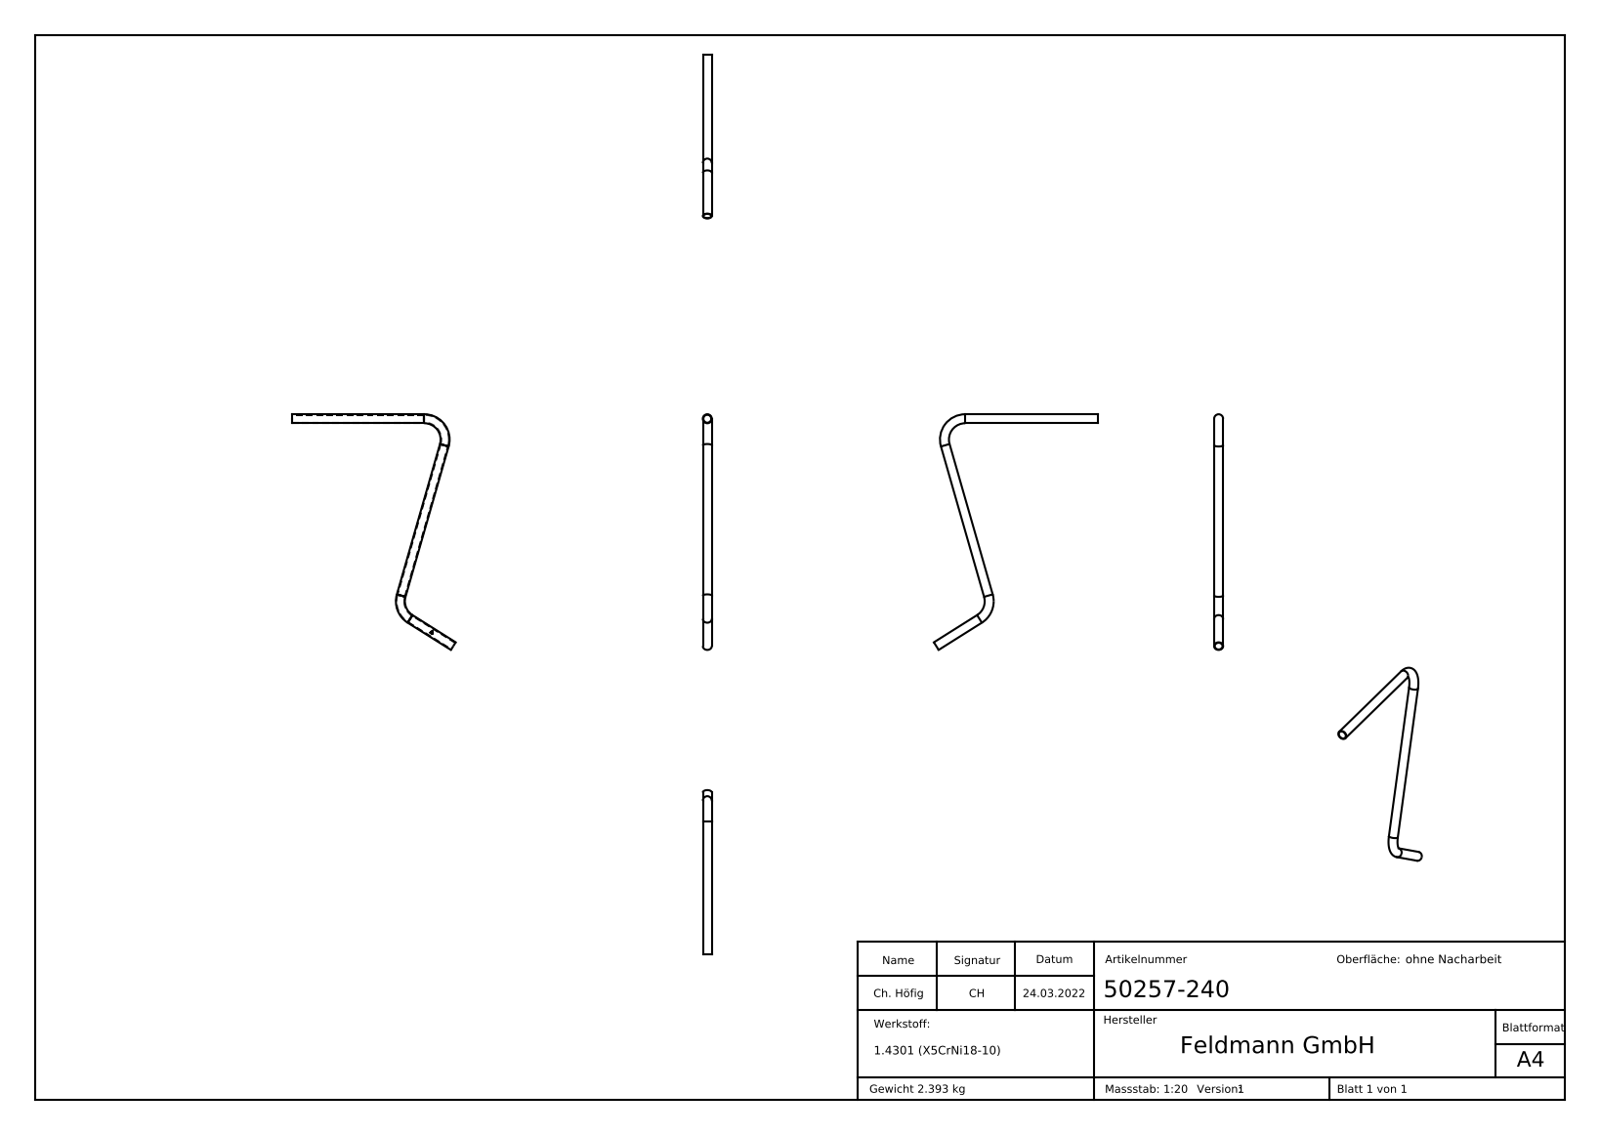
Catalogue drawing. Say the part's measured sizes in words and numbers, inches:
The part is named "50257-240". Its 3-D file was written by "SolidWorks 2018 (CONFIG_CONTROL_DESIGN)". It is 1 solid with 275 faces: 103 planar, 30 cylindrical and 142 other. Overall it measures 34.827 by 24.219 by 1.327 inches. Its volume is 18.49 cubic inches and its surface area 470.2 square inches. Round holes: 3 of diameter 1.169. Round bosses or shafts: 3 of diameter 1.327. Partial cylindrical surfaces (rounded edges, fillets, slot ends): 1 of radius 0.589. The main face-to-face distances are 0.052, 0.117, 0.046, 0.159, 0.047, 0.144, 0.128, 0.287, 0.154, 0.054.
